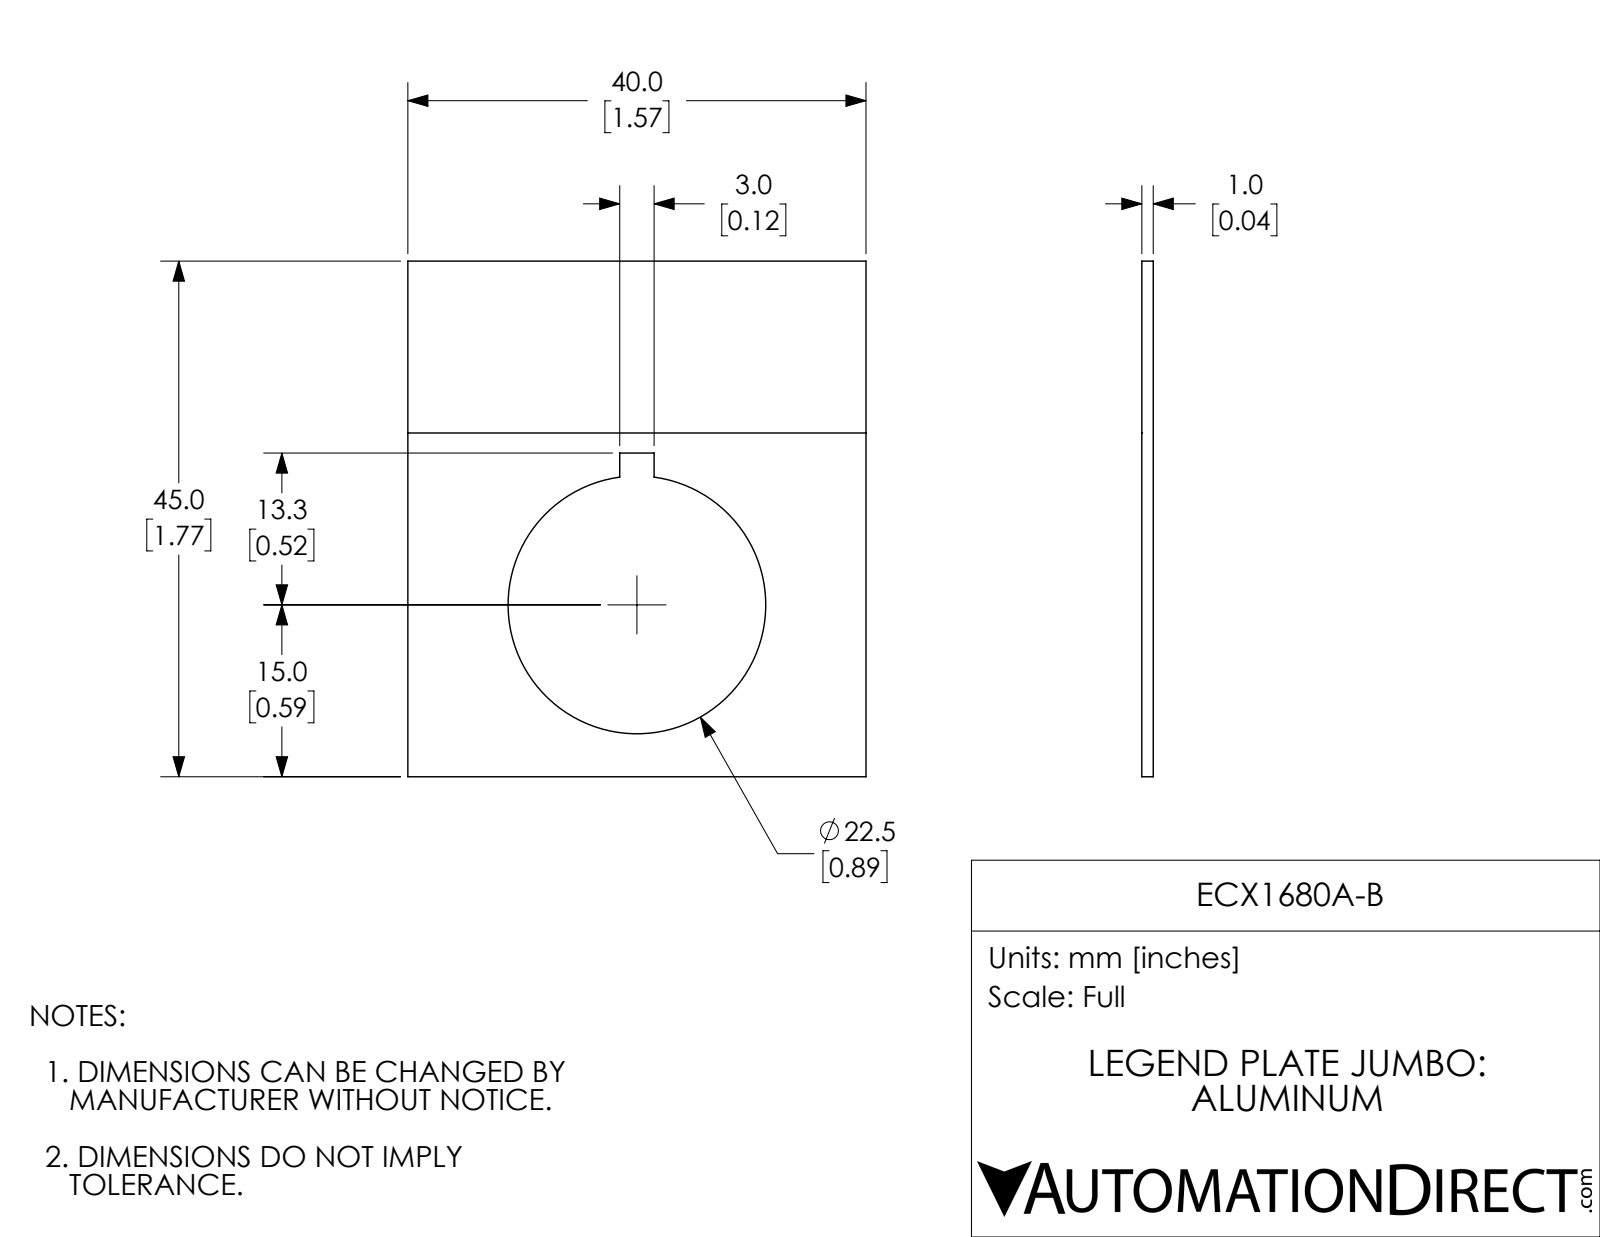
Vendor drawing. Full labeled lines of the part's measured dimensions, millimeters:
Part name (STEP PRODUCT): ECX1680A-B
STEP written by: SolidWorks 2017 (AUTOMOTIVE_DESIGN)
Units: millimetres
Bodies: 1 solid, 14 faces (11 planar, 3 cylindrical, 0 other)
Overall size (bounding box): 45 × 40 × 1
Volume: 1 393 mm³ · Surface area: 3 037 mm²
Round holes (diameter × count): ⌀22.5 ×1
Main face-to-face distances: 1, 0.99, 40, 45, 18.5, 21.5, 28.25, 16.75, 3, 30
